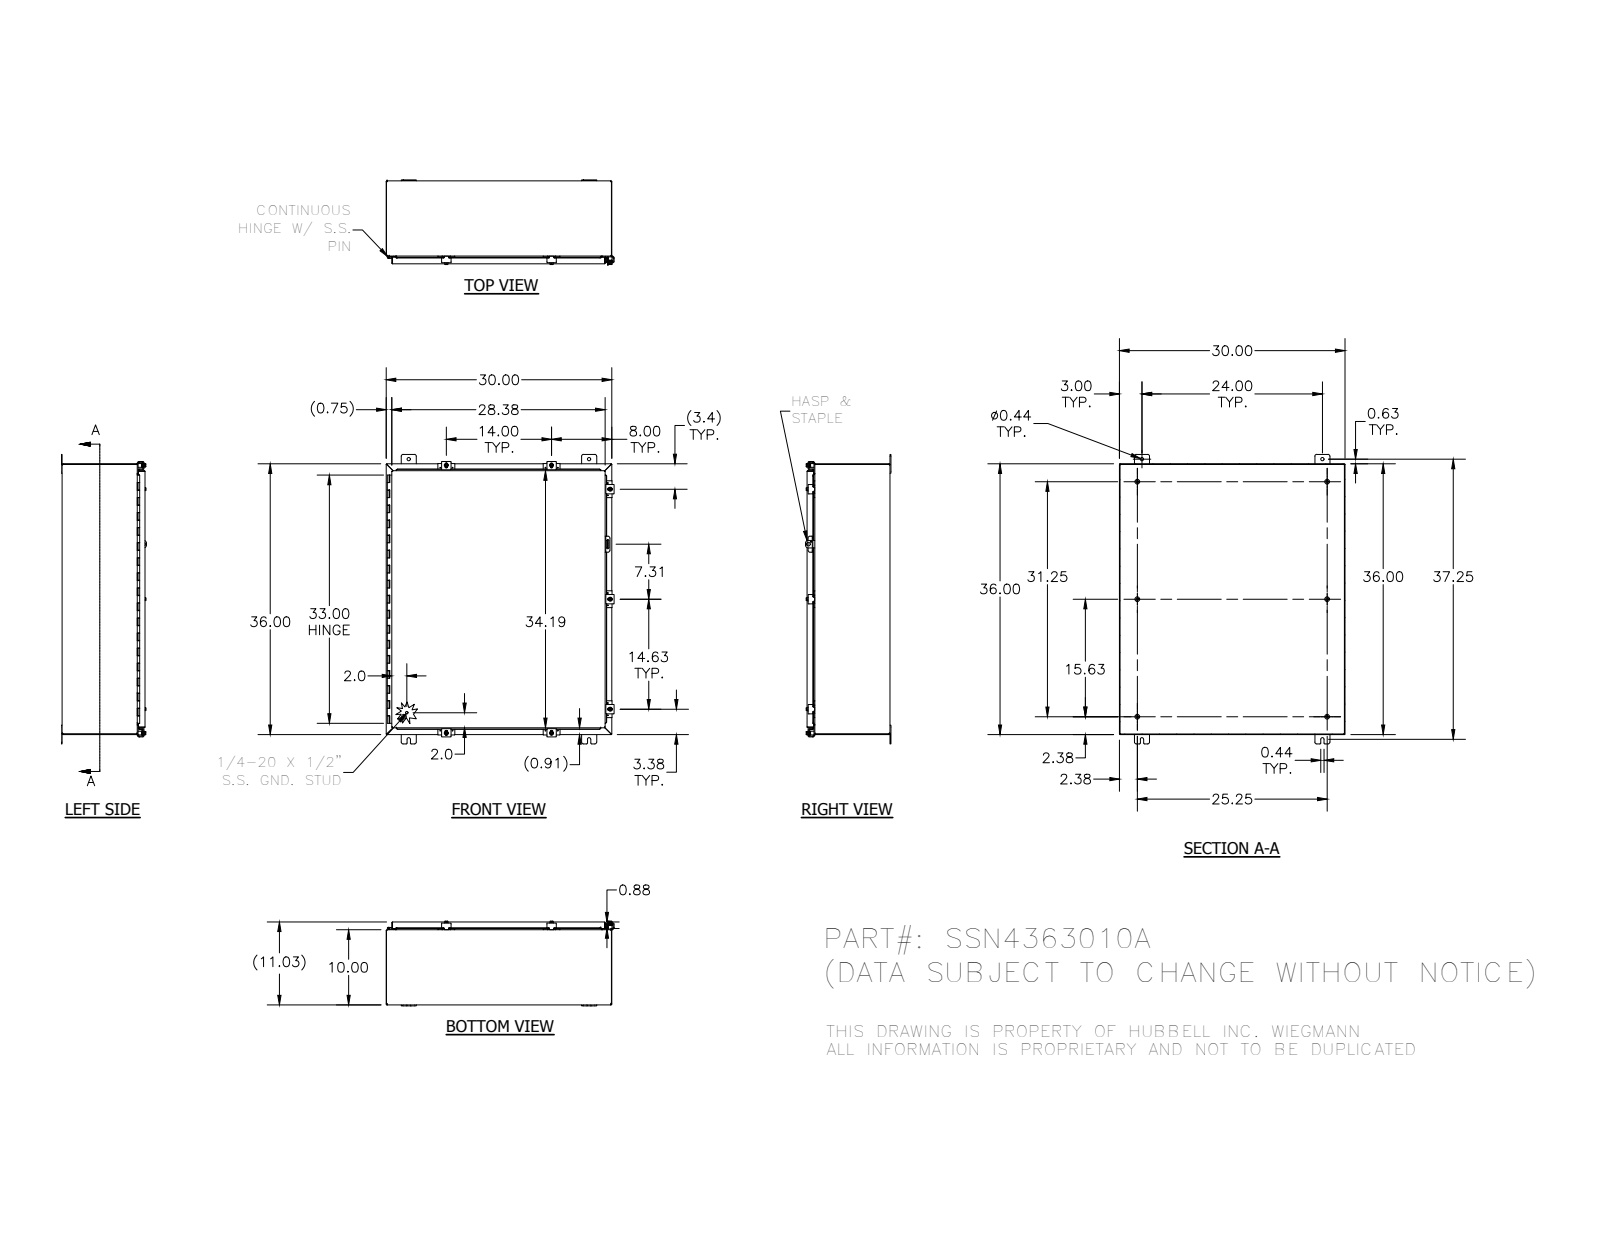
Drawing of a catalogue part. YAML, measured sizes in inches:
part_name: "30824-2; 32874-36; SSN43630ALID; 38859 (+8 more)"
step_written_by: "SolidWorks 2014 (AUTOMOTIVE_DESIGN)"
units: inches
bodies: {solids: 54, faces: 2180, planar: 862, cylindrical: 947, other: 371}
overall_size: [38.5, 30.216, 11.355]
volume: 302.3
surface_area: 7985
round_holes:
  - {diameter: 0.11, count: 14}
  - {diameter: 0.211, count: 7}
  - {diameter: 0.281, count: 7}
  - {diameter: 0.3, count: 7}
  - {diameter: 0.438, count: 4}
  - {diameter: 0.125, count: 1}
  - {diameter: 0.156, count: 1}
  - {diameter: 0.5, count: 1}
round_bosses_or_shafts:
  - {diameter: 0.25, count: 9}
  - {diameter: 0.52, count: 7}
  - {diameter: 0.5, count: 7}
  - {diameter: 0.35, count: 7}
  - {diameter: 0.625, count: 6}
  - {diameter: 0.33, count: 6}
  - {diameter: 0.337, count: 1}
  - {diameter: 0.12, count: 1}
partial_cylinders:
  - {radius: 0.03, count: 83}
  - {radius: 0.125, count: 37}
  - {radius: 0.25, count: 33}
  - {radius: 0.031, count: 23}
  - {radius: 0.105, count: 23}
  - {radius: 0.062, count: 18}
  - {radius: 0.141, count: 14}
  - {radius: 0.1, count: 10}
face_to_face_distances: [0.074, 10.959, 10.885, 11.033, 29.926, 35.926, 29.852, 30, 9.926, 1.033]
hole_center_spacings: [0.876, 35.298, 14, 1.625, 13.191, 14.625, 14.816, 15.441]
